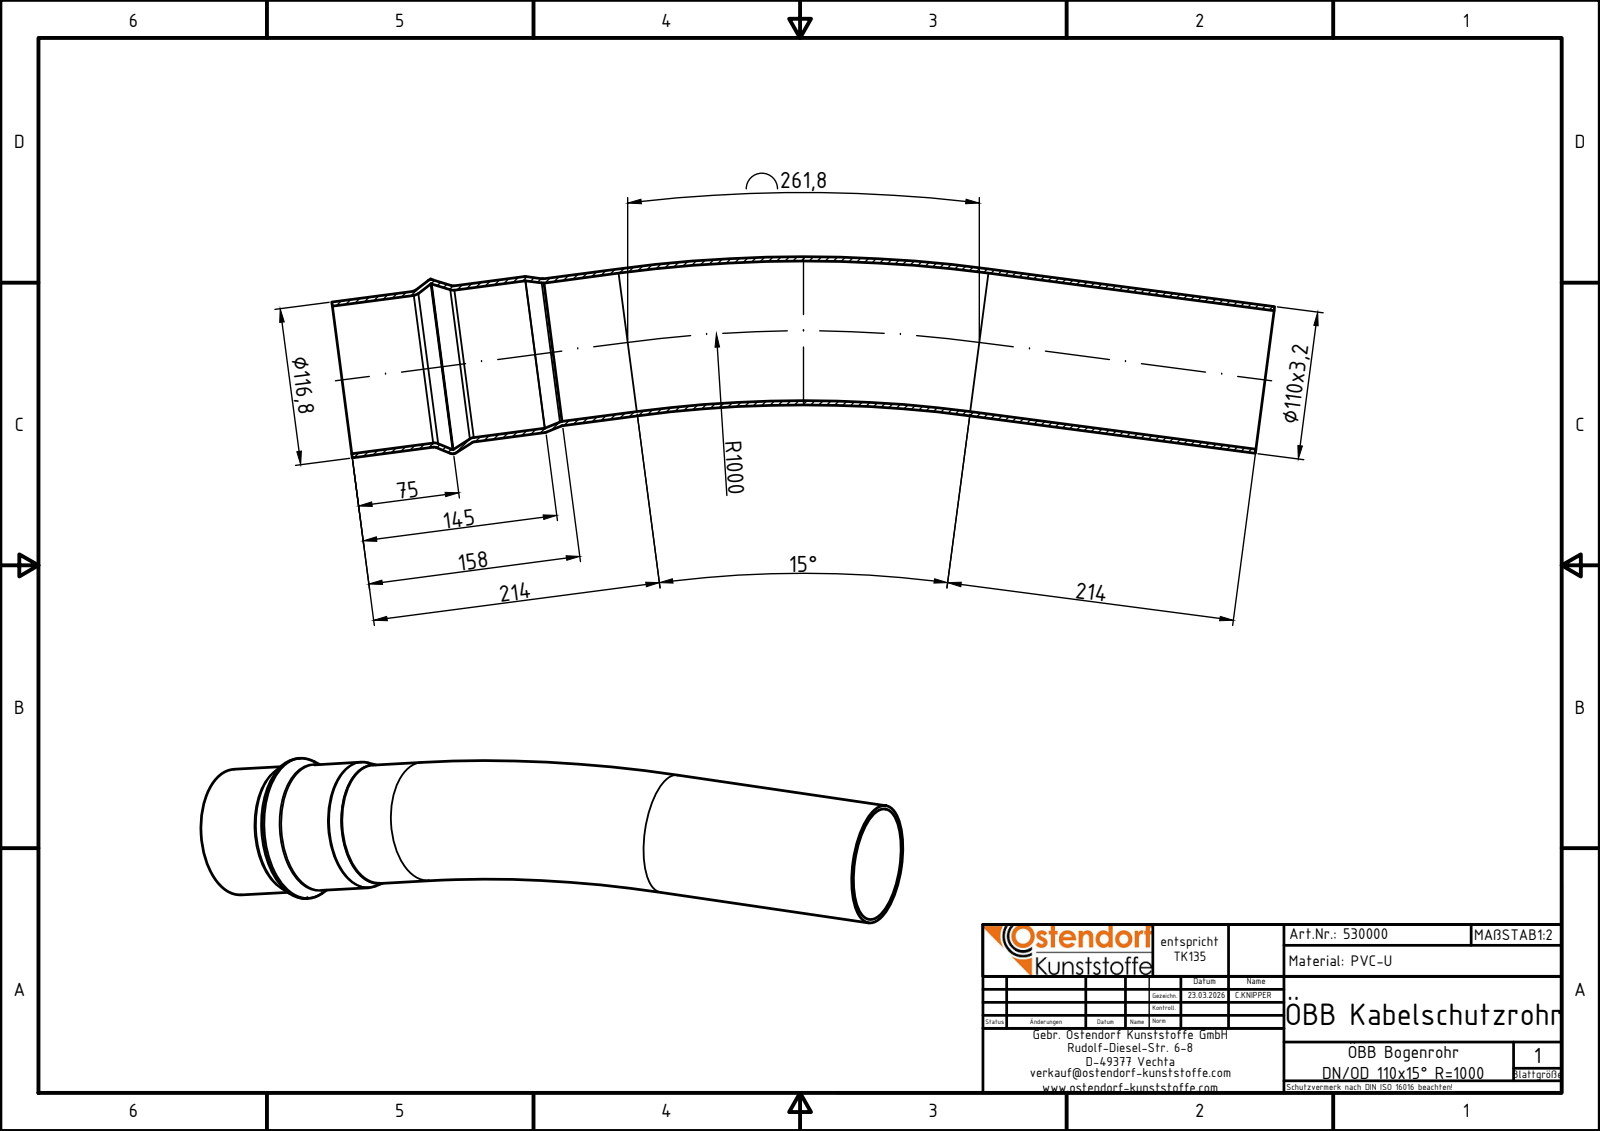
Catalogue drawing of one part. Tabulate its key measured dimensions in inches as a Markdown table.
| quantity | value |
| --- | --- |
| part name | 530000z |
| STEP written by | Autodesk Inventor 2024 (AUTOMOTIVE_DESIGN) |
| units | inches |
| bodies | 1 solid, 32 faces (2 planar, 10 cylindrical, 20 other) |
| overall size | 27.313 × 8.183 × 5.138 |
| volume | 46.25 in³ |
| surface area | 737.1 in² |
| round holes (diameter × count) | 4.078 × 2, 4.346 × 1, 4.886 × 1 |
| round bosses / shafts (diameter × count) | 4.331 × 2, 5.138 × 1, 4.598 × 1 |
